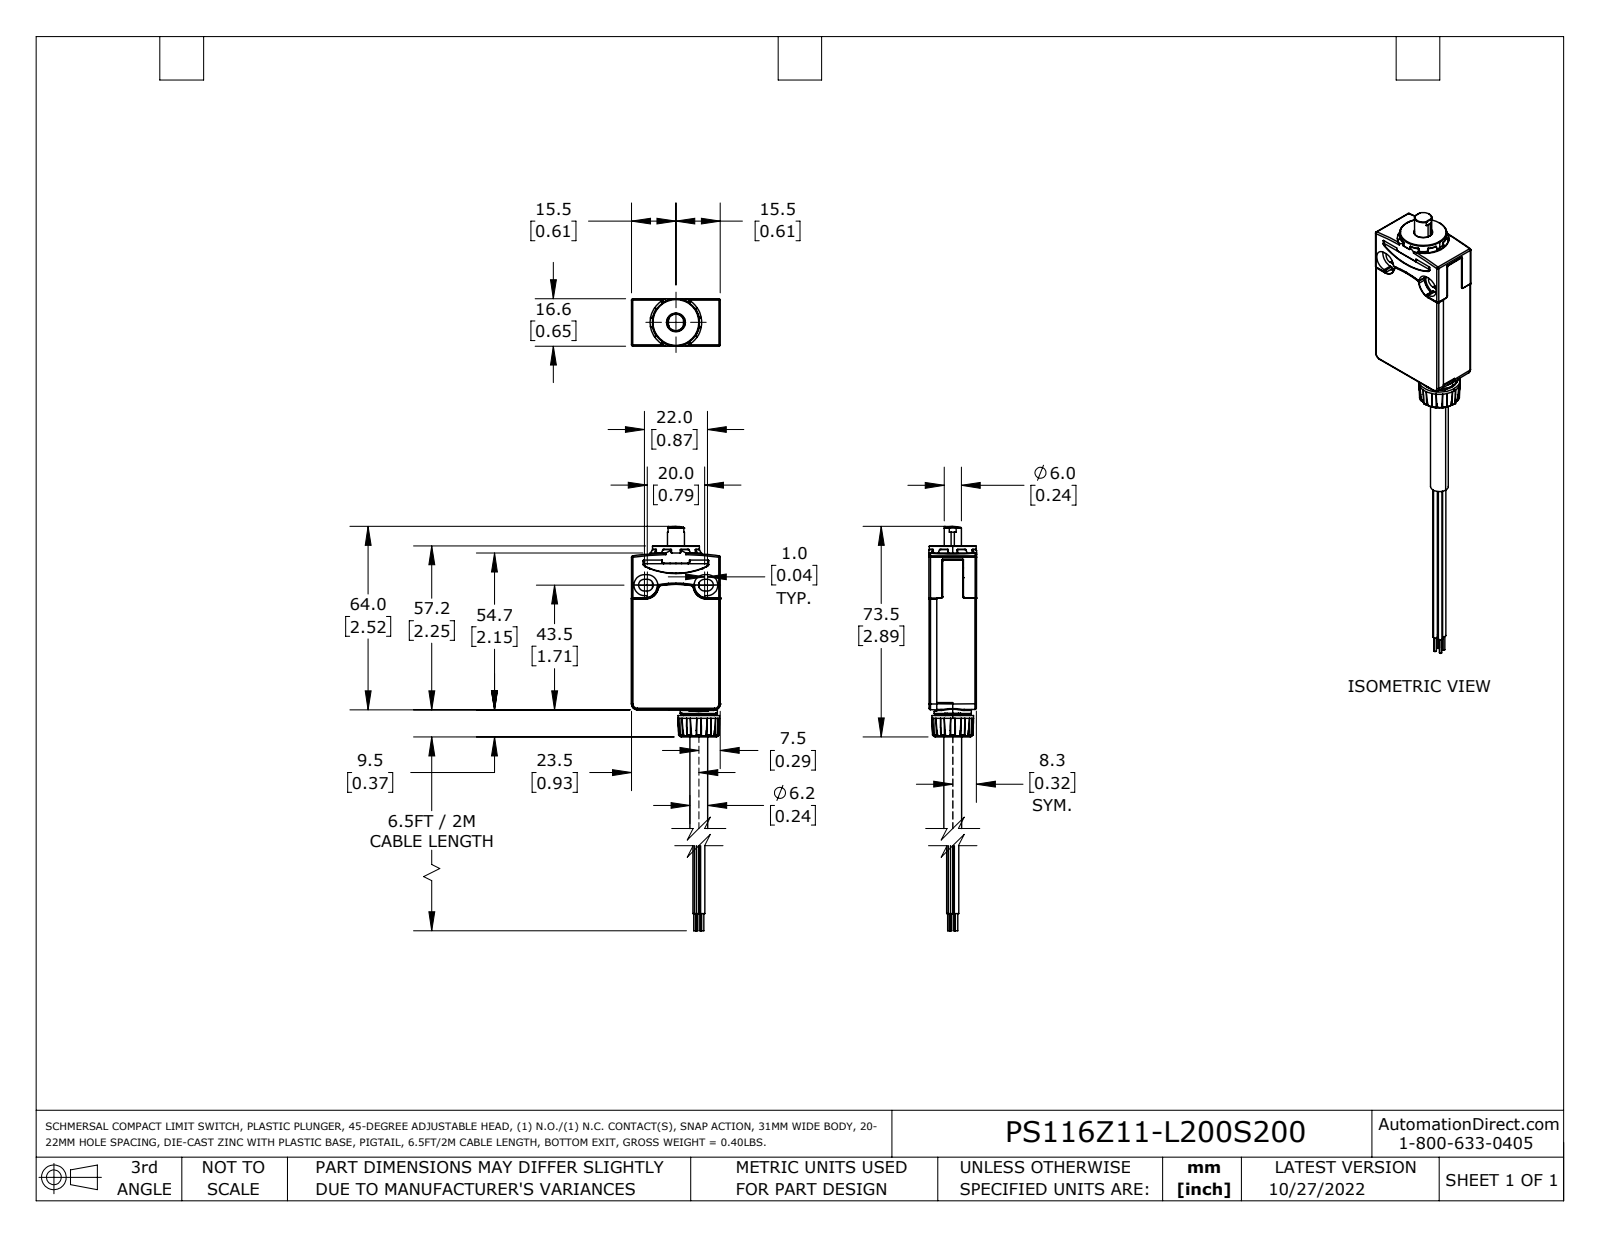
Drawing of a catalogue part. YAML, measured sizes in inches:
part_name: "PS116Z11-L200S200_Default"
step_written_by: "SolidWorks 2021 (CONFIG_CONTROL_DESIGN)"
units: inches
bodies: {solids: 1, faces: 1000, planar: 313, cylindrical: 408, other: 279}
overall_size: [7.145, 1.22, 0.654]
volume: 1.831
surface_area: 19.37
round_holes:
  - {diameter: 0.079, count: 2}
  - {diameter: 0.244, count: 1}
  - {diameter: 0.252, count: 1}
  - {diameter: 0.48, count: 1}
  - {diameter: 0.571, count: 1}
round_bosses_or_shafts:
  - {diameter: 0.059, count: 4}
  - {diameter: 0.031, count: 4}
  - {diameter: 0.512, count: 2}
  - {diameter: 0.646, count: 1}
  - {diameter: 0.571, count: 1}
  - {diameter: 0.567, count: 1}
  - {diameter: 0.524, count: 1}
  - {diameter: 0.244, count: 1}
partial_cylinders:
  - {radius: 0.008, count: 134}
  - {radius: 0.004, count: 61}
  - {radius: 0.02, count: 30}
  - {radius: 0.014, count: 10}
  - {radius: 0.039, count: 8}
  - {radius: 0.012, count: 6}
  - {radius: 0.079, count: 5}
  - {radius: 0.081, count: 4}
face_to_face_distances: [0.65, 0.652, 1.22, 0.118, 0.654, 0.197, 0.177, 0.356, 0.535, 0.116]
hole_center_spacings: [0.315]
